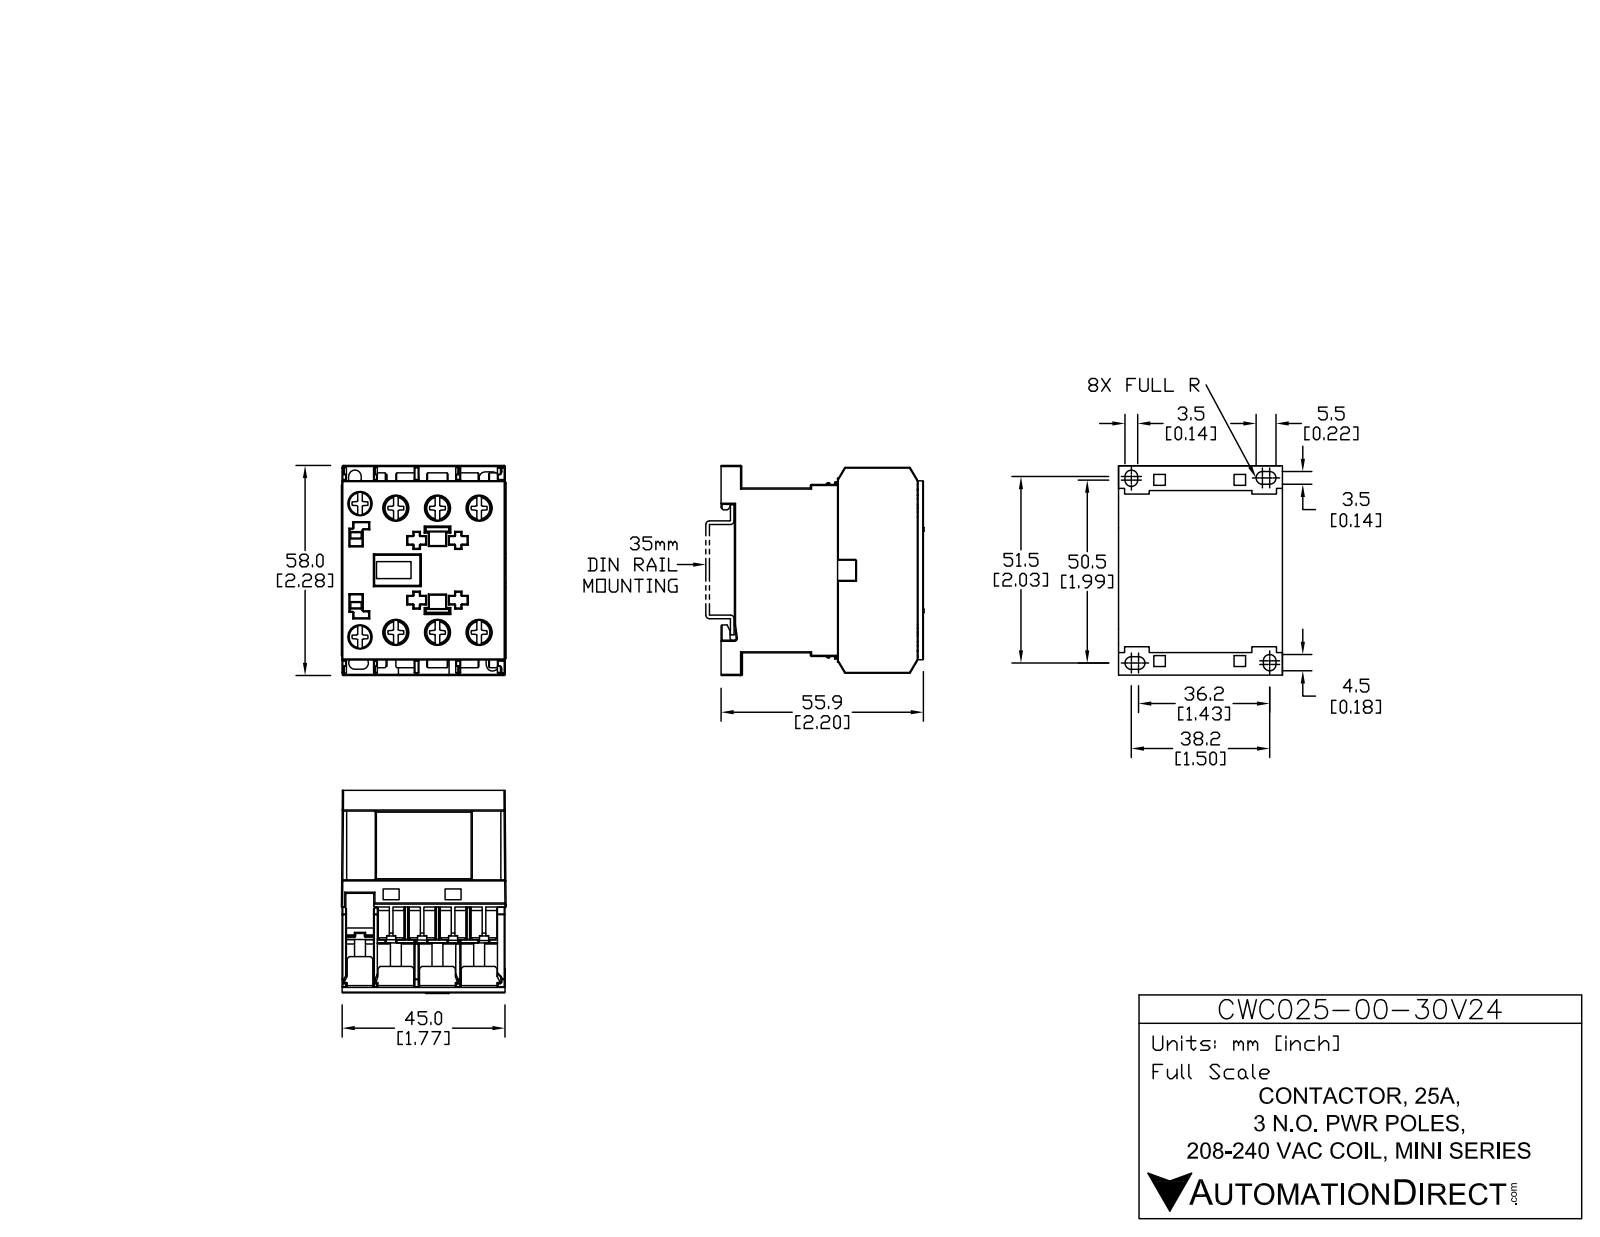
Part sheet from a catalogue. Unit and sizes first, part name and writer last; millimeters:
Units: millimetres
Overall size (bounding box): 58 × 55.7 × 45
Round holes (diameter × count): ⌀6.85 ×6, ⌀6.5 ×2
Round bosses / shafts (diameter × count): ⌀6.5 ×6, ⌀3.5 ×6, ⌀5.25 ×2, ⌀2.75 ×2
Partial cylindrical surfaces — rounded edges, fillets, slot ends (radius × count): R0.2 ×14, R0.5 ×10, R1.72 ×8, R0.3 ×7
Main face-to-face distances: 45, 1, 23.5, 28.5, 28.53, 52, 23.47, 37.35, 8.85, 8.82
Hole centre spacings: 11.5, 36.37, 34.5, 9.55, 21.02, 23, 32.52, 36.75
Volume: 92 387 mm³ · Surface area: 34 434 mm²
Bodies: 2 solids, 746 faces (639 planar, 107 cylindrical, 0 other)
Part name (STEP PRODUCT): CWC025-00-30V24
STEP written by: SolidWorks 2013 (AUTOMOTIVE_DESIGN)
